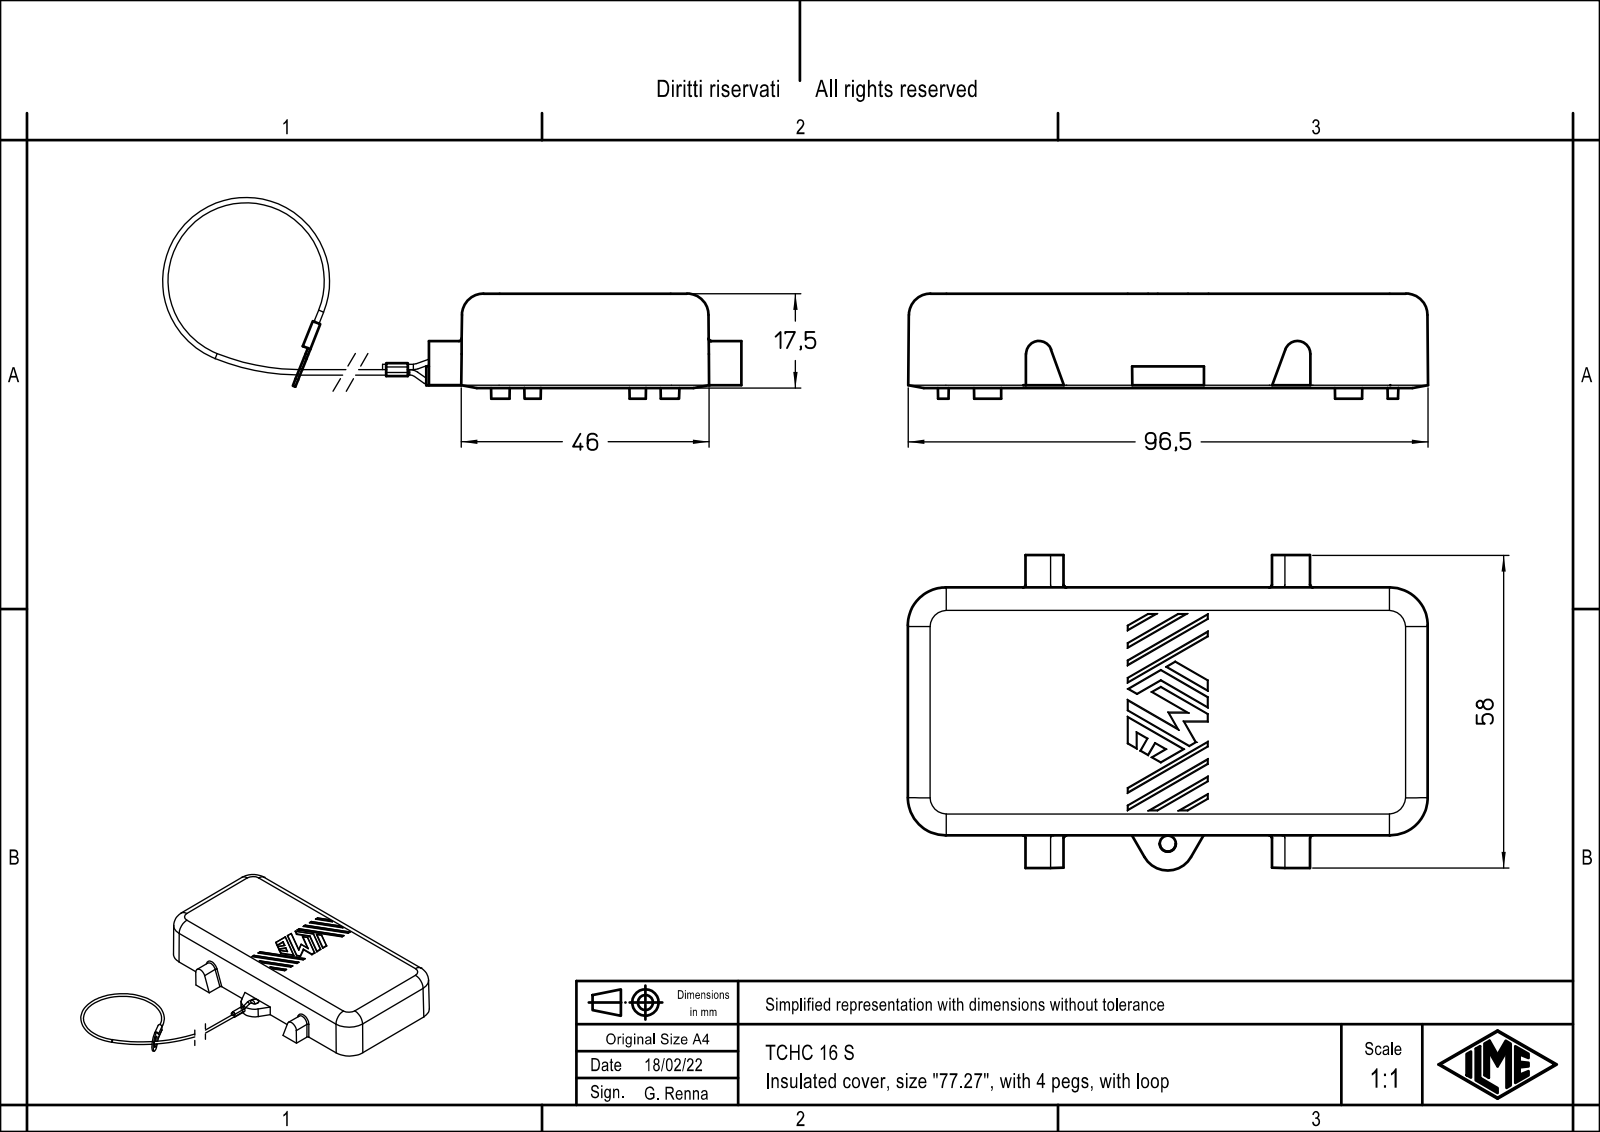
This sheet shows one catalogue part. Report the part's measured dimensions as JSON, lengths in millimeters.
{"part_name": "TCHC_16_S", "step_written_by": "Creo Elements/Direct Modeling 20.1B 02-Apr-2019 (C) Parametric Technology GmbH (AUTOMOTIVE_DESIGN)", "units": "millimeters", "bodies": {"solids": 1, "faces": 282, "planar": 117, "cylindrical": 116, "other": 49}, "overall_size": [228.27, 96.49, 19.65], "volume_mm3": 42214, "surface_area_mm2": 18168, "round_holes": [[3, 1], [4.2, 1]], "round_bosses_or_shafts": [[1, 5], [7, 1]], "partial_cylinders_radius": [[0.15, 44], [1.5, 4], [4, 4], [7, 4], [0.7, 2], [0.75, 2], [1.25, 2], [2.4, 2]], "face_to_face_distances": [5.5, 5.51, 7, 11.49, 16.99, 6.99, 17.14, 5.65, 15.78, 19.5]}
